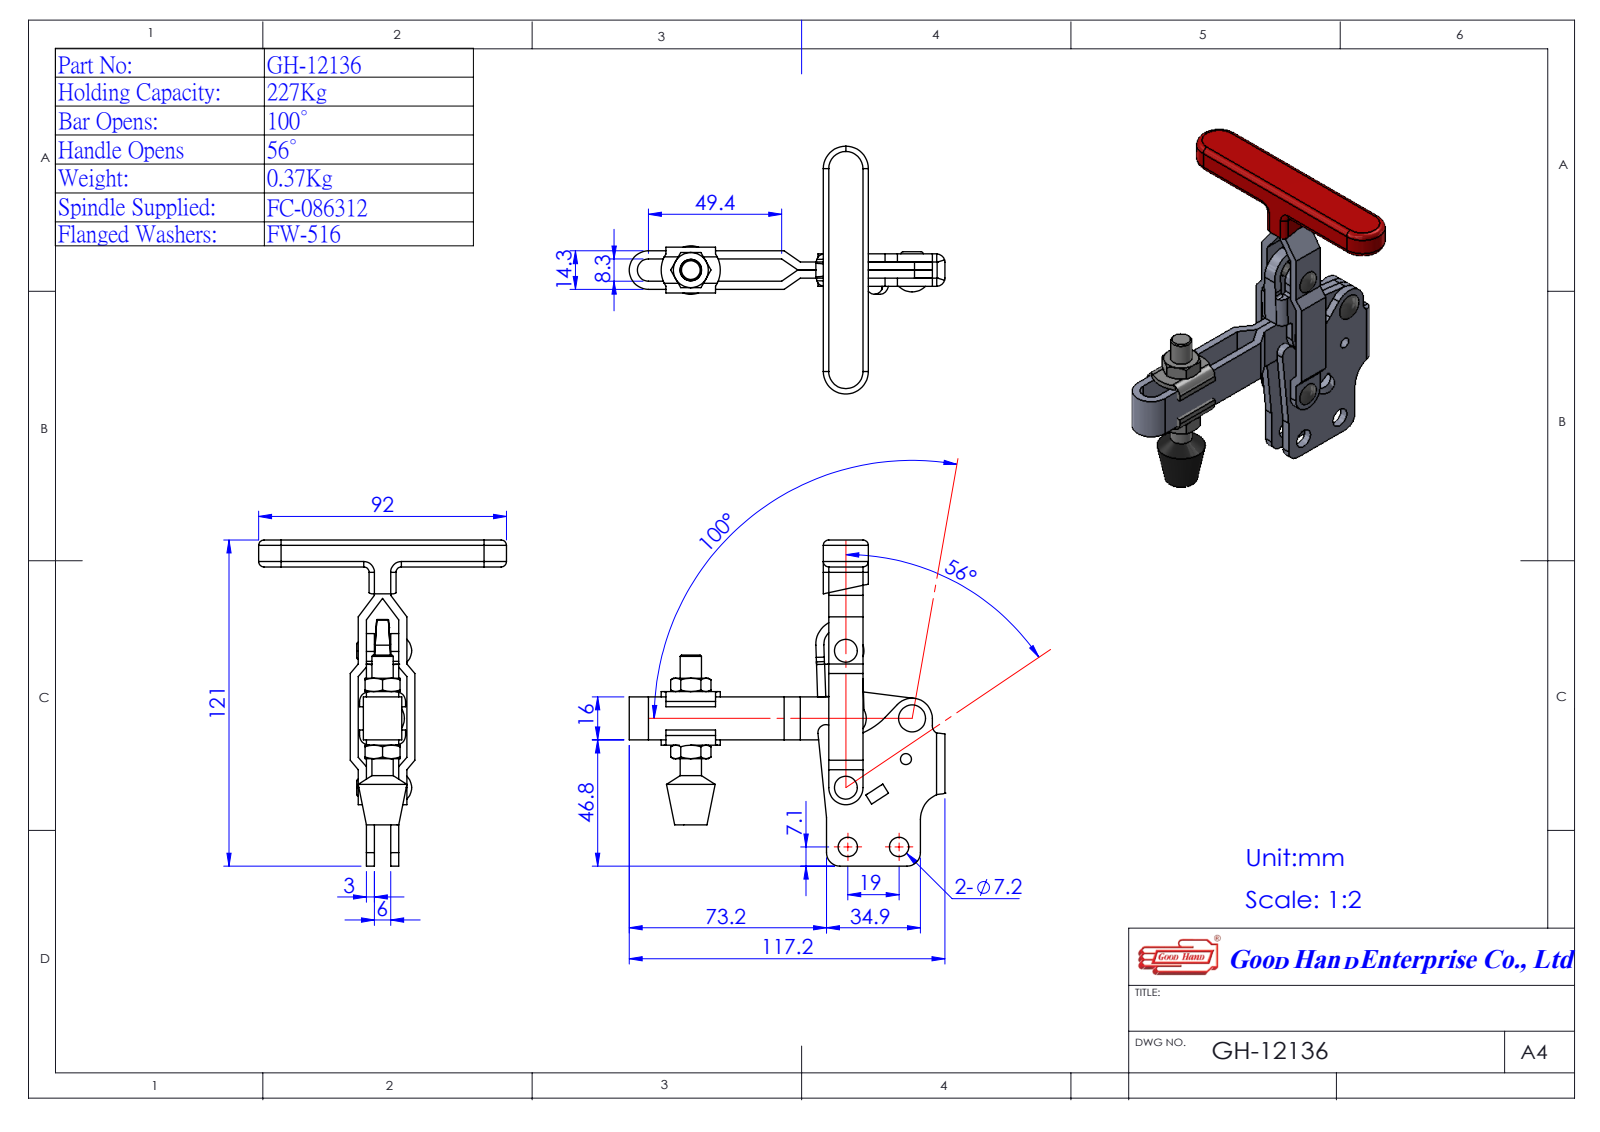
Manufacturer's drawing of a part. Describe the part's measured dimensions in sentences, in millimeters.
The part is named "Group4^GH-12136(簡化); Group2^GH-12136(簡化); Group5^GH-12136(簡化); 11213009-1^GH-12130 (+2 more)". Its 3-D file was written by "SolidWorks 2016 (AUTOMOTIVE_DESIGN)". It is 5 solids with 320 faces: 158 planar, 106 cylindrical and 56 other. Overall it measures 121 by 117.19 by 92 millimeters. Its volume is 58 949 cubic millimeters and its surface area 37 634 square millimeters. Round holes: 5 of diameter 4, 2 of diameter 7.2. Round bosses or shafts: 2 of diameter 6.4, 1 of diameter 7.93, 1 of diameter 6.3. Partial cylindrical surfaces (rounded edges, fillets, slot ends): 4 of radius 1.5, 4 of radius 7.5, 2 of radius 0.1, 2 of radius 1, 2 of radius 2, 2 of radius 3, 2 of radius 3.1, 2 of radius 6.4. The main face-to-face distances are 3, 6, 9, 12, 1.15, 4.15, 7.15, 10.15, 13.15, 1.85. The hole center spacings are 15.27, 19, 22.01, 23.4, 24.69, 25.13, 25.73, 25.95.
